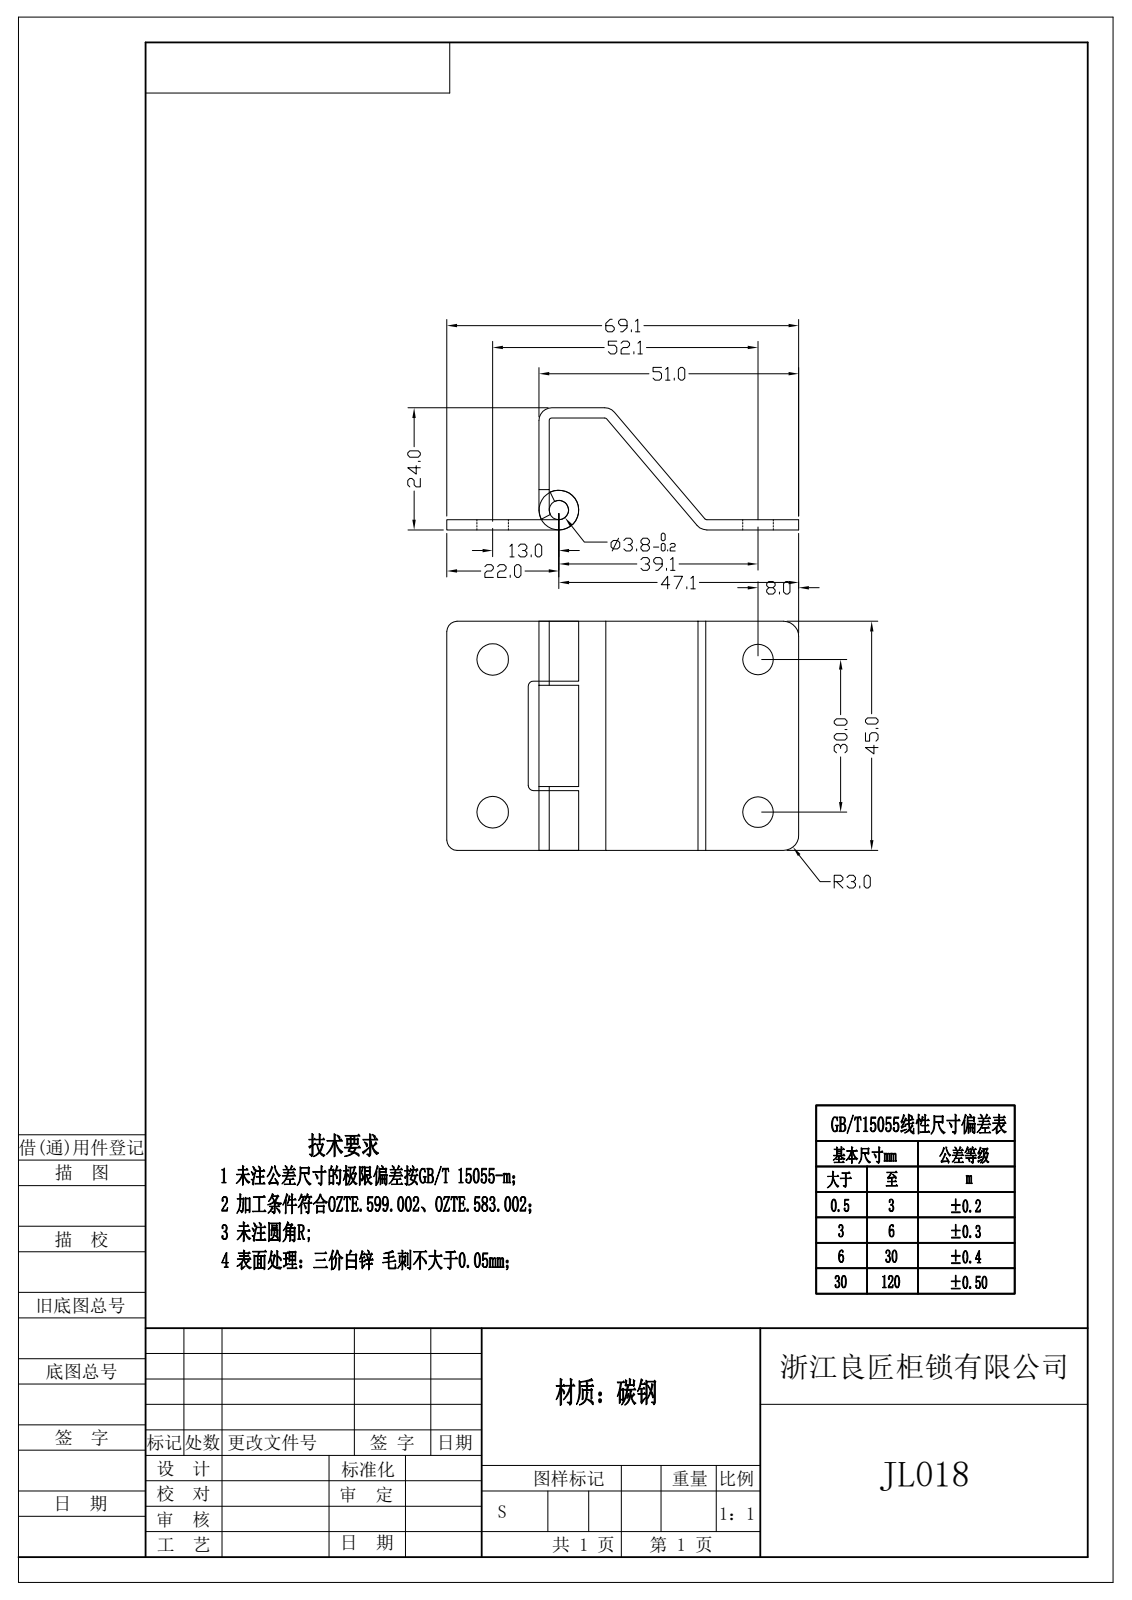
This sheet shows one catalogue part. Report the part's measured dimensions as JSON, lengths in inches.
{"step_written_by": "Rhino 8.5 (CONFIG_CONTROL_DESIGN)", "units": "inches", "bodies": {"solids": 3, "faces": 84, "planar": 46, "cylindrical": 32, "other": 6}, "overall_size": [2.72, 1.909, 0.945], "volume_in3": 0.61, "surface_area_in2": 17.7, "round_holes": [[0.236, 2], [0.244, 2], [0.15, 1]], "round_bosses_or_shafts": [[0.307, 1], [0.276, 1], [0.157, 1], [0.138, 1]], "partial_cylinders_radius": [[0.079, 4], [0.02, 3], [0.098, 3], [0.039, 2]], "face_to_face_distances": [0.079, 0.871, 0.793, 0.945, 0.866, 0.074, 1.772, 0.463, 1.309, 2.72], "hole_center_spacings": [1.181, 2.051, 2.367]}
